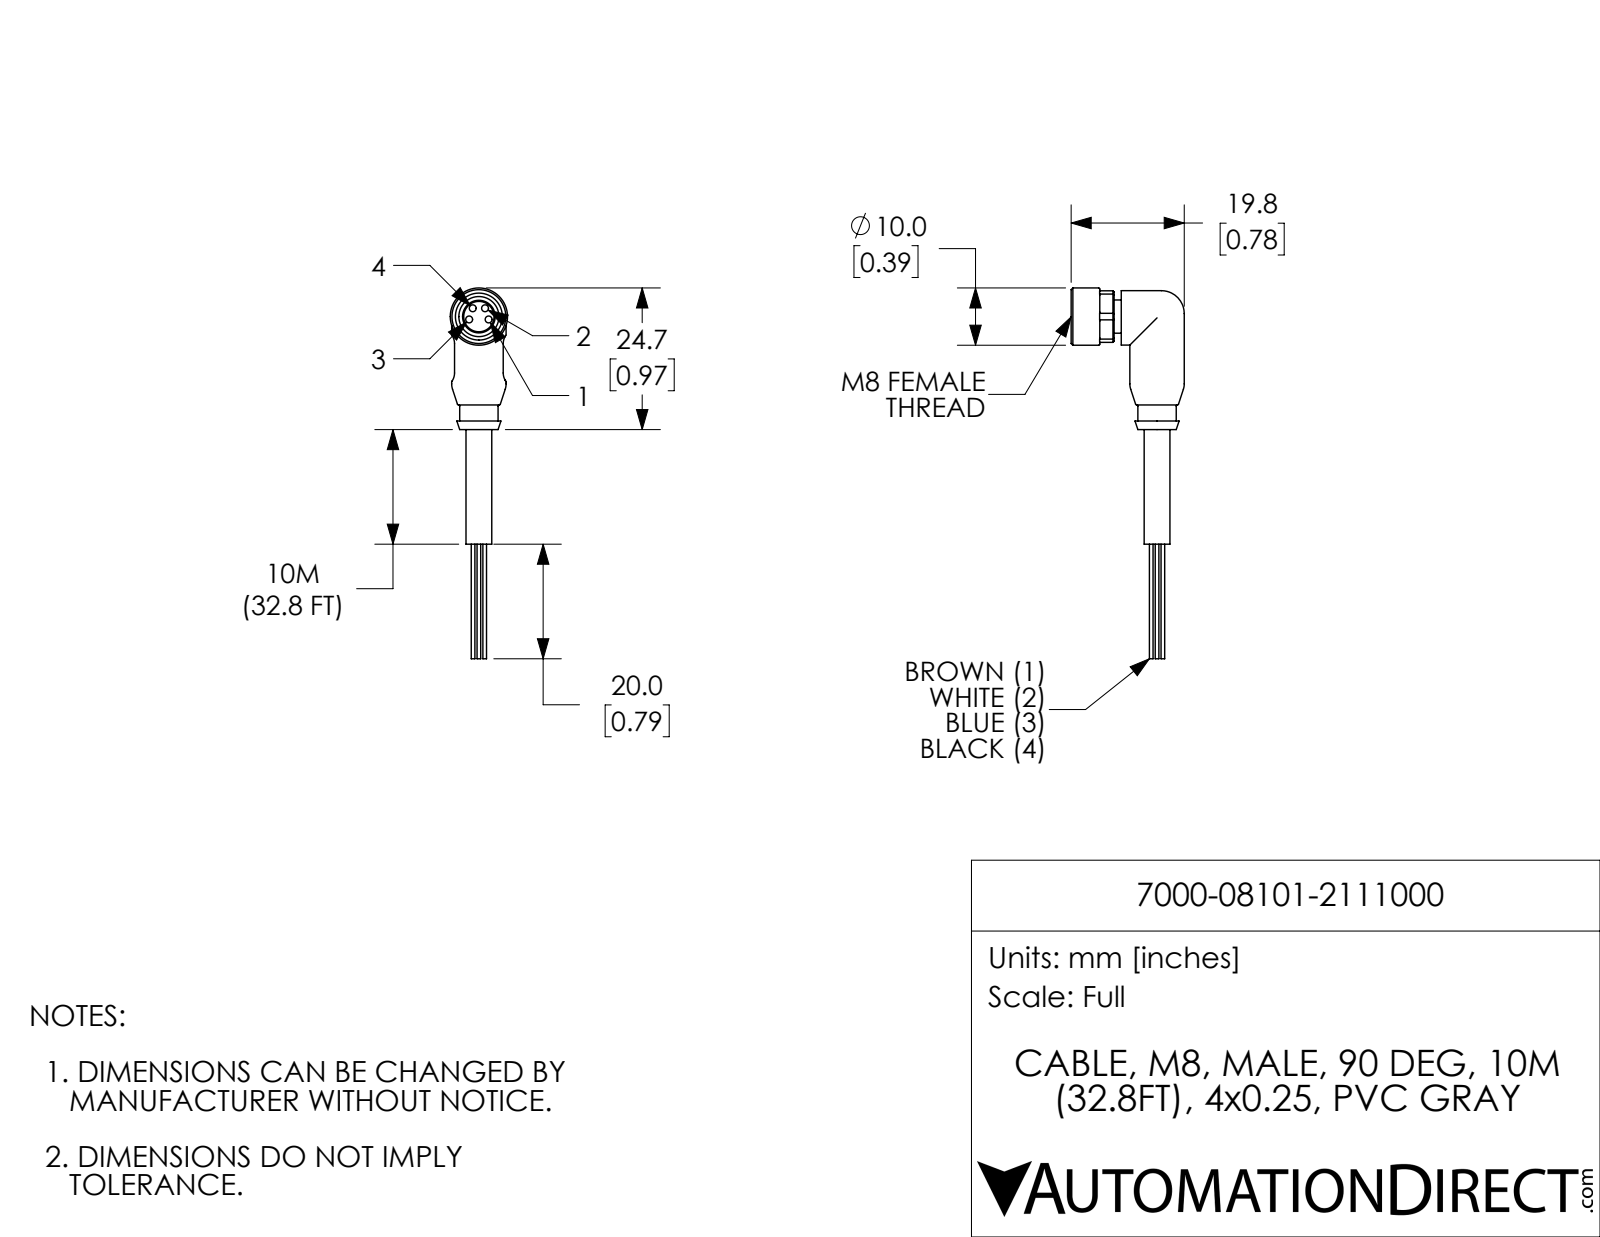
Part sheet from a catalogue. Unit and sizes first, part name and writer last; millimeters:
Units: millimetres
Overall size (bounding box): 64.7 × 19.8 × 10
Round holes (diameter × count): ⌀1.2 ×4, ⌀7 ×1
Round bosses / shafts (diameter × count): ⌀0.6 ×3, ⌀9.5 ×2, ⌀10 ×1, ⌀6.7 ×1, ⌀5.8 ×1, ⌀5.7 ×1, ⌀4.5 ×1, ⌀0.6 ×1
Partial cylindrical surfaces — rounded edges, fillets, slot ends (radius × count): R0.2 ×4, R2.5 ×4, R4.9 ×1
Main face-to-face distances: 1.2, 9, 1.5, 8.5, 0.7, 20, 6.8, 8.1, 7.5, 8.7
Hole centre spacings: 1.8, 1.8, 2.1, 3.4, 2.1, 3.4
Volume: 2 410 mm³ · Surface area: 1 920 mm²
Bodies: 5 solids, 117 faces (41 planar, 47 cylindrical, 29 other)
Part name (STEP PRODUCT): 7000-08101-2111000
STEP written by: SolidWorks 2017 (AUTOMOTIVE_DESIGN)
